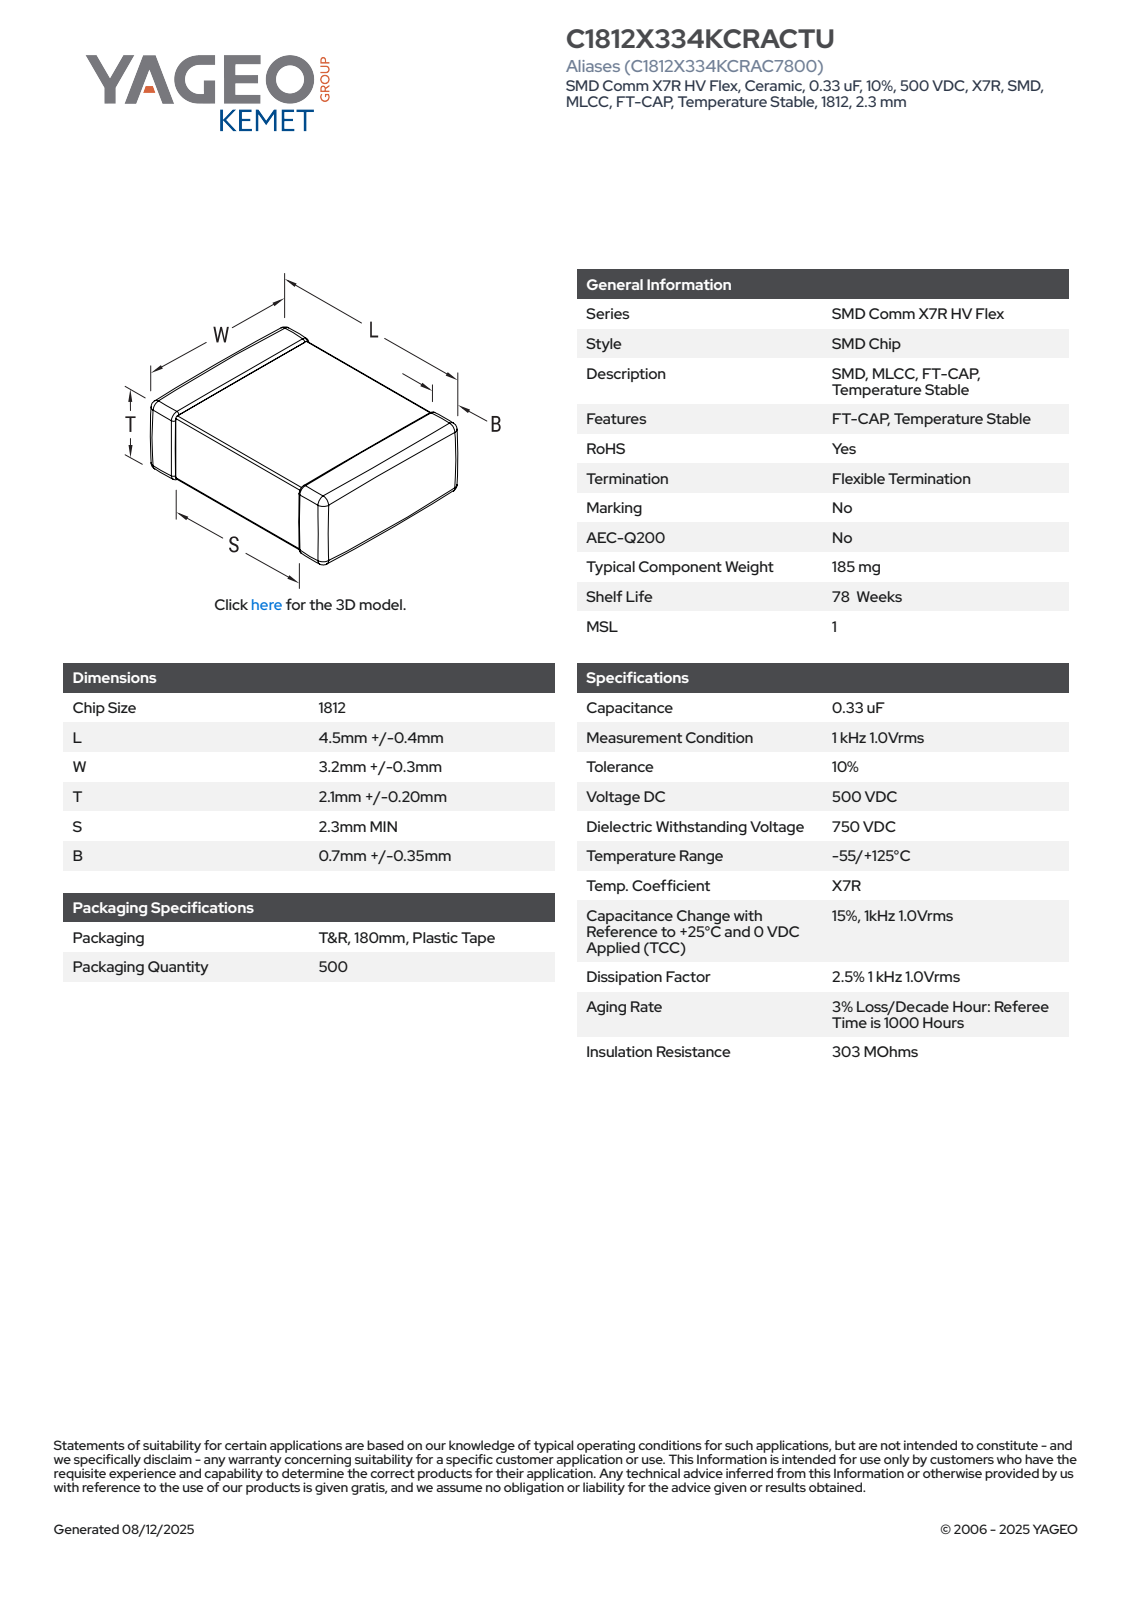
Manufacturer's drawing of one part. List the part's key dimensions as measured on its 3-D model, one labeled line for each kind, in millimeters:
Part name (STEP PRODUCT): CCS_CCSTDNOS_1812_L4.9W3.5T2.3B1.05
STEP written by: SolidWorks 2014 (AUTOMOTIVE_DESIGN)
Units: millimetres
Bodies: 4 solids, 121 faces (71 planar, 34 cylindrical, 16 other)
Overall size (bounding box): 4.9 × 3.5 × 2.3
Volume: 37 mm³ · Surface area: 72 mm²
Main face-to-face distances: 2.23, 2.16, 3.43, 4.9, 2.3, 3.36, 3.5, 1.42, 1.94, 1.49
